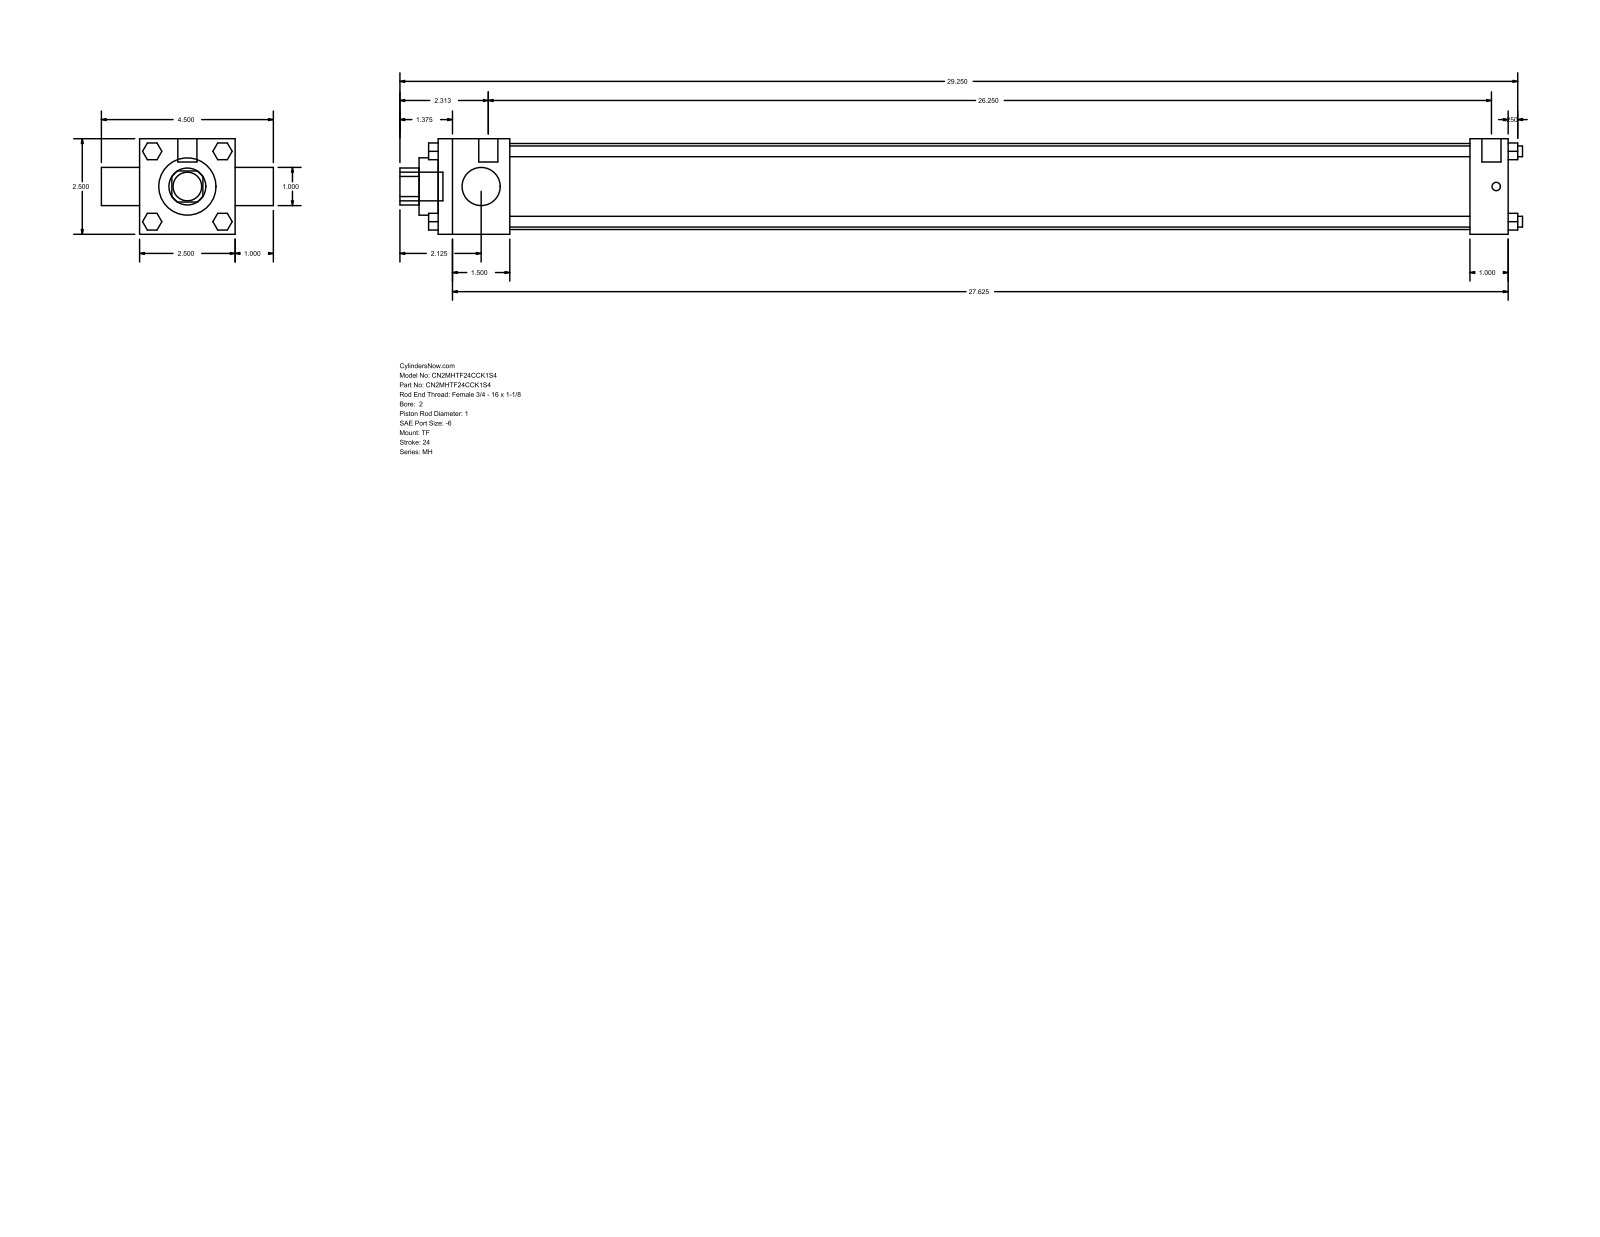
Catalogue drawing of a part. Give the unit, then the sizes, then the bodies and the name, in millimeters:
Units: millimetres
Overall size (bounding box): 746.12 × 114.3 × 63.5
Round holes (diameter × count): ⌀25.4 ×2, ⌀38.1 ×1, ⌀57.15 ×1
Round bosses / shafts (diameter × count): ⌀7.14 ×4, ⌀5.56 ×3, ⌀12.7 ×2, ⌀19.05 ×1
Partial cylindrical surfaces — rounded edges, fillets, slot ends (radius × count): R12.29 ×1
Main face-to-face distances: 63.5, 711.2, 25.4, 47.63, 685.8, 638.17, 663.57, 88.9, 723.9, 6.35
Bodies: 0 solids, 120 faces (92 planar, 28 cylindrical, 0 other)
Part name (STEP PRODUCT): MH_TF__0200_1
STEP written by: GSSL Pune (CONFIG_CONTROL_DESIGN)
